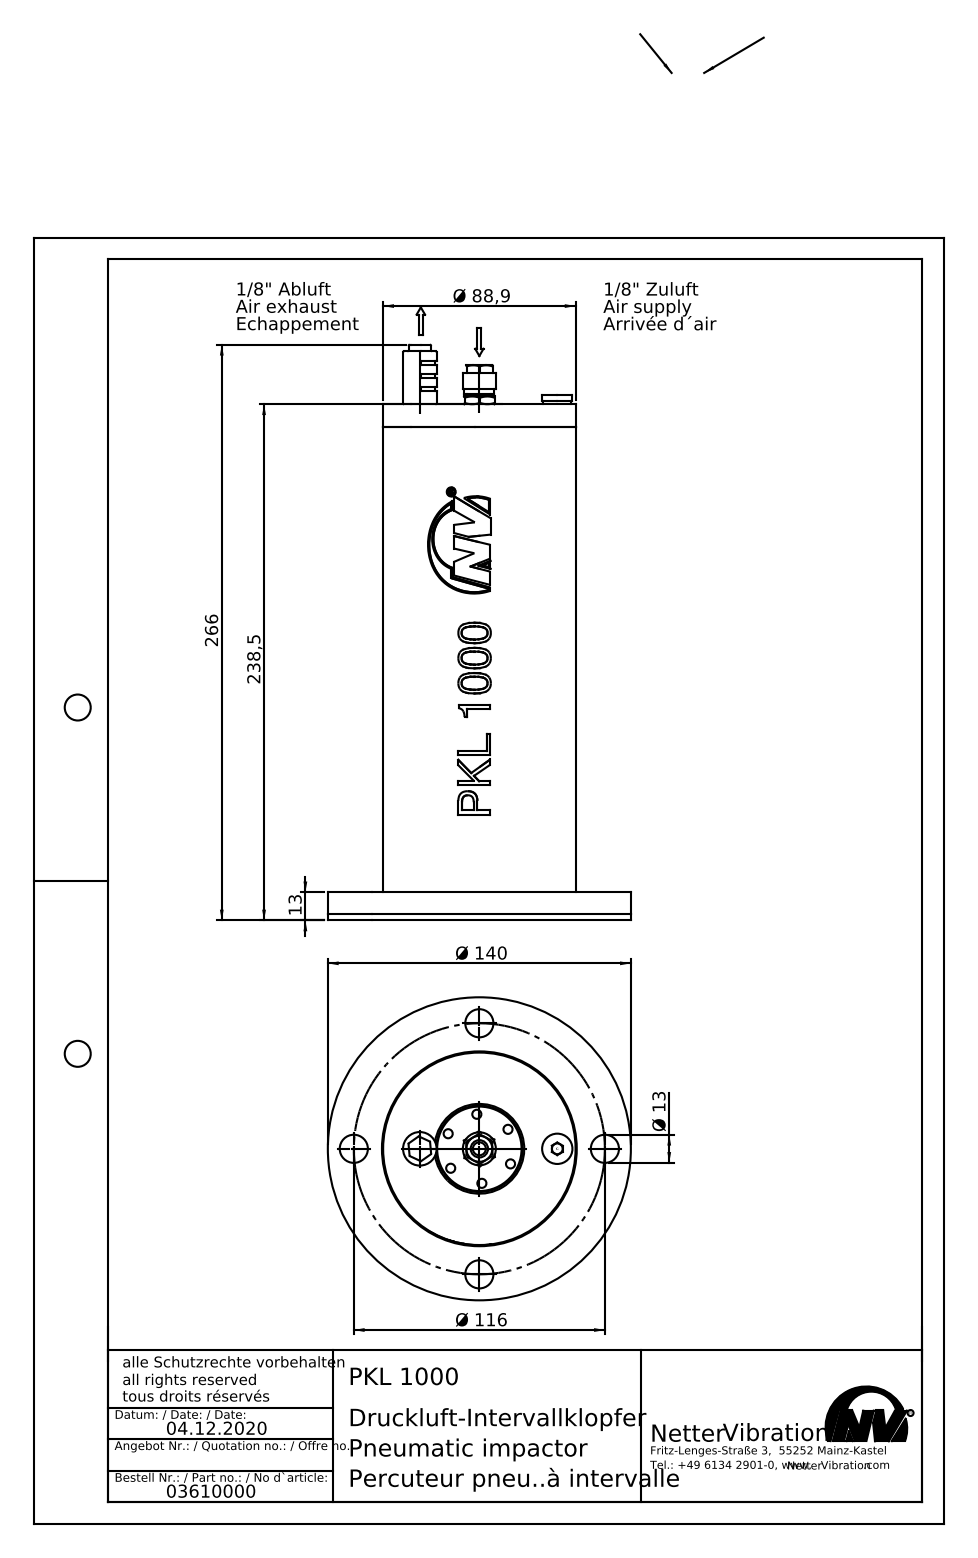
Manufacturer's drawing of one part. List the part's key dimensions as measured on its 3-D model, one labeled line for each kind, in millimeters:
Part name (STEP PRODUCT): PKL 1000
STEP written by: SolidWorks 2015 (CONFIG_CONTROL_DESIGN)
Units: millimetres
Bodies: 11 solids, 530 faces (133 planar, 157 cylindrical, 240 other)
Overall size (bounding box): 266 × 140 × 140
Volume: 1 746 000 mm³ · Surface area: 179 500 mm²
Round holes (diameter × count): ⌀4.2 ×6, ⌀13 ×4, ⌀6 ×2, ⌀6.81 ×1, ⌀8 ×1, ⌀8.57 ×1, ⌀10 ×1, ⌀34.4 ×1, ⌀41.7 ×1, ⌀53.5 ×1, ⌀56 ×1, ⌀90 ×1
Round bosses / shafts (diameter × count): ⌀9.73 ×2, ⌀140 ×1, ⌀88.9 ×1, ⌀86 ×1, ⌀60 ×1, ⌀57.1 ×1, ⌀53 ×1, ⌀47 ×1
Partial cylindrical surfaces — rounded edges, fillets, slot ends (radius × count): R0.5 ×18, R7 ×1, R44.55 ×1
Main face-to-face distances: 215.5, 3, 10, 10.5, 9.5, 20, 13, 12.5, 0.5, 226
Hole centre spacings: 16, 27.71, 58, 82.02, 32, 27.72, 42.25, 43.49
